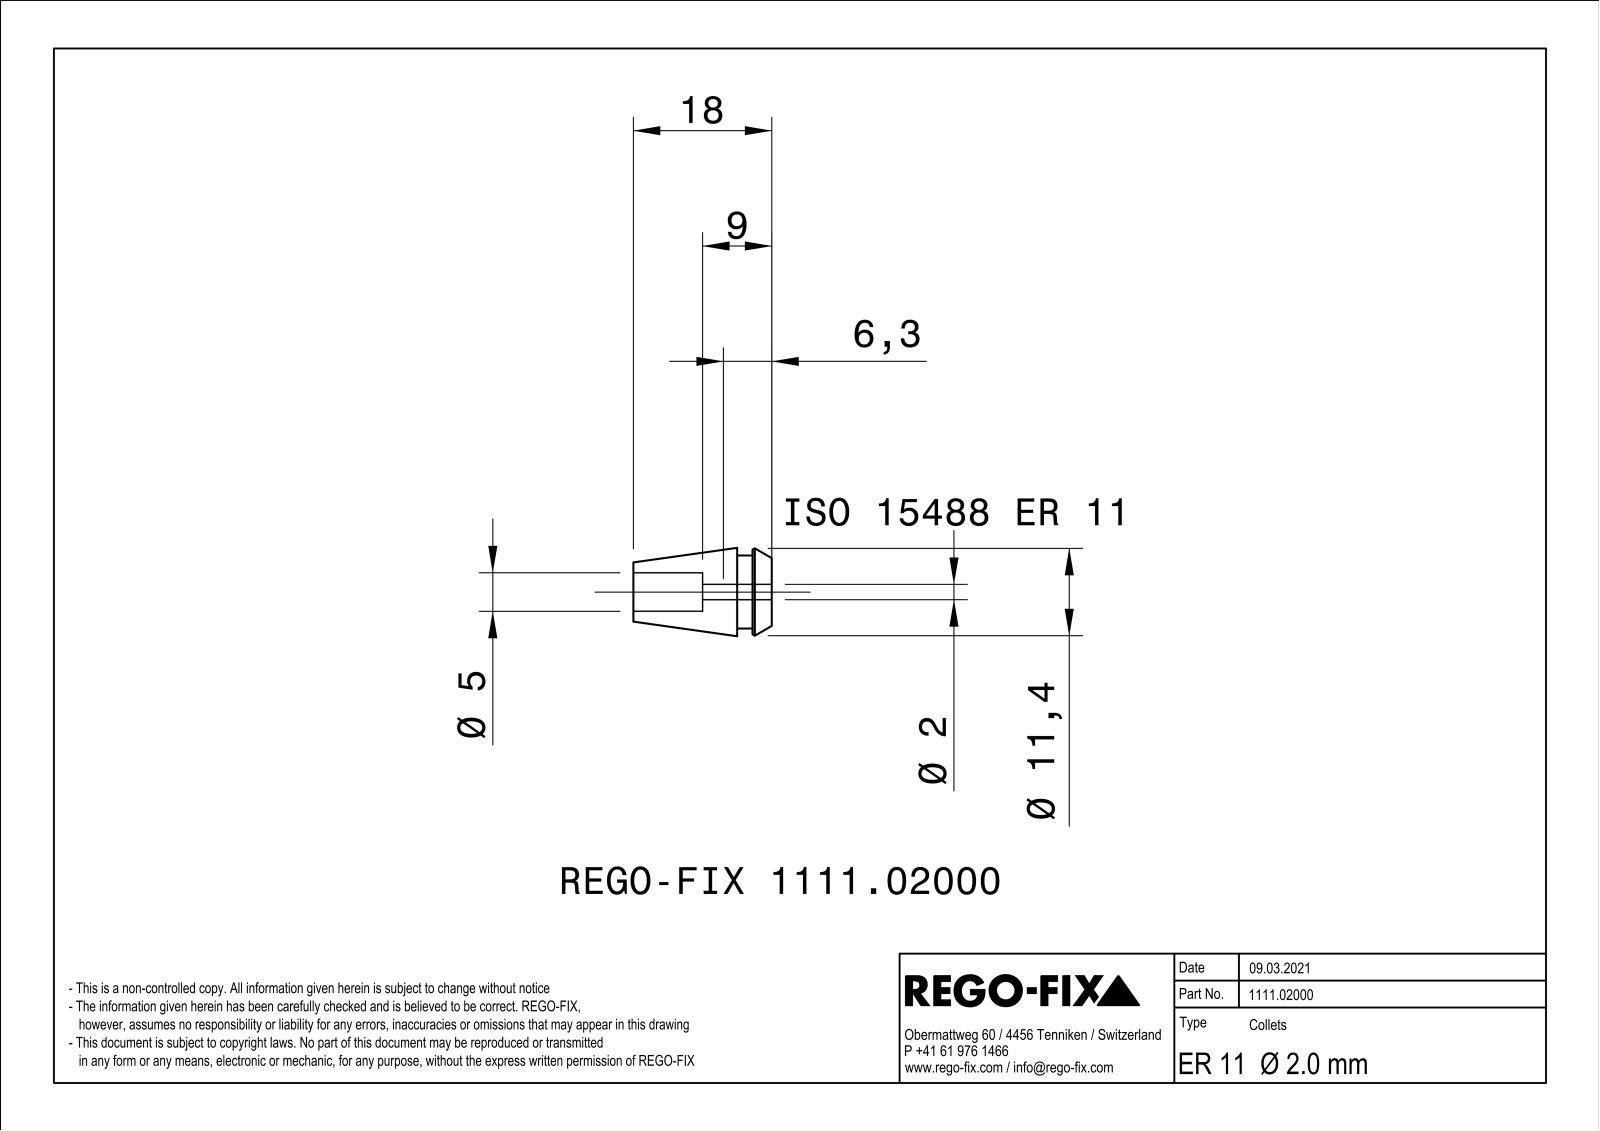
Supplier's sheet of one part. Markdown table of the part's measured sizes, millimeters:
| quantity | value |
| --- | --- |
| part name | NOCUT |
| STEP written by | SIEMENS PLM Software Solid Edge ST10 (AUTOMOTIVE_DESIGN) |
| units | millimeters |
| bodies | 1 solid, 291 faces (77 planar, 65 cylindrical, 149 other) |
| overall size | 18 × 11.43 × 11.43 |
| volume | 837 mm³ |
| surface area | 2 046 mm² |
| round holes (diameter × count) | 2 × 1 |
| round bosses / shafts (diameter × count) | 11.44 × 1 |
| partial cylindrical surfaces (radius × count) | 0.23 × 24, 2.5 × 1, 4.75 × 1 |
| main face-to-face distances | 0.46, 0.44, 4.5, 2.5, 2, 9, 18, 15.5, 13.5, 6.5 |
